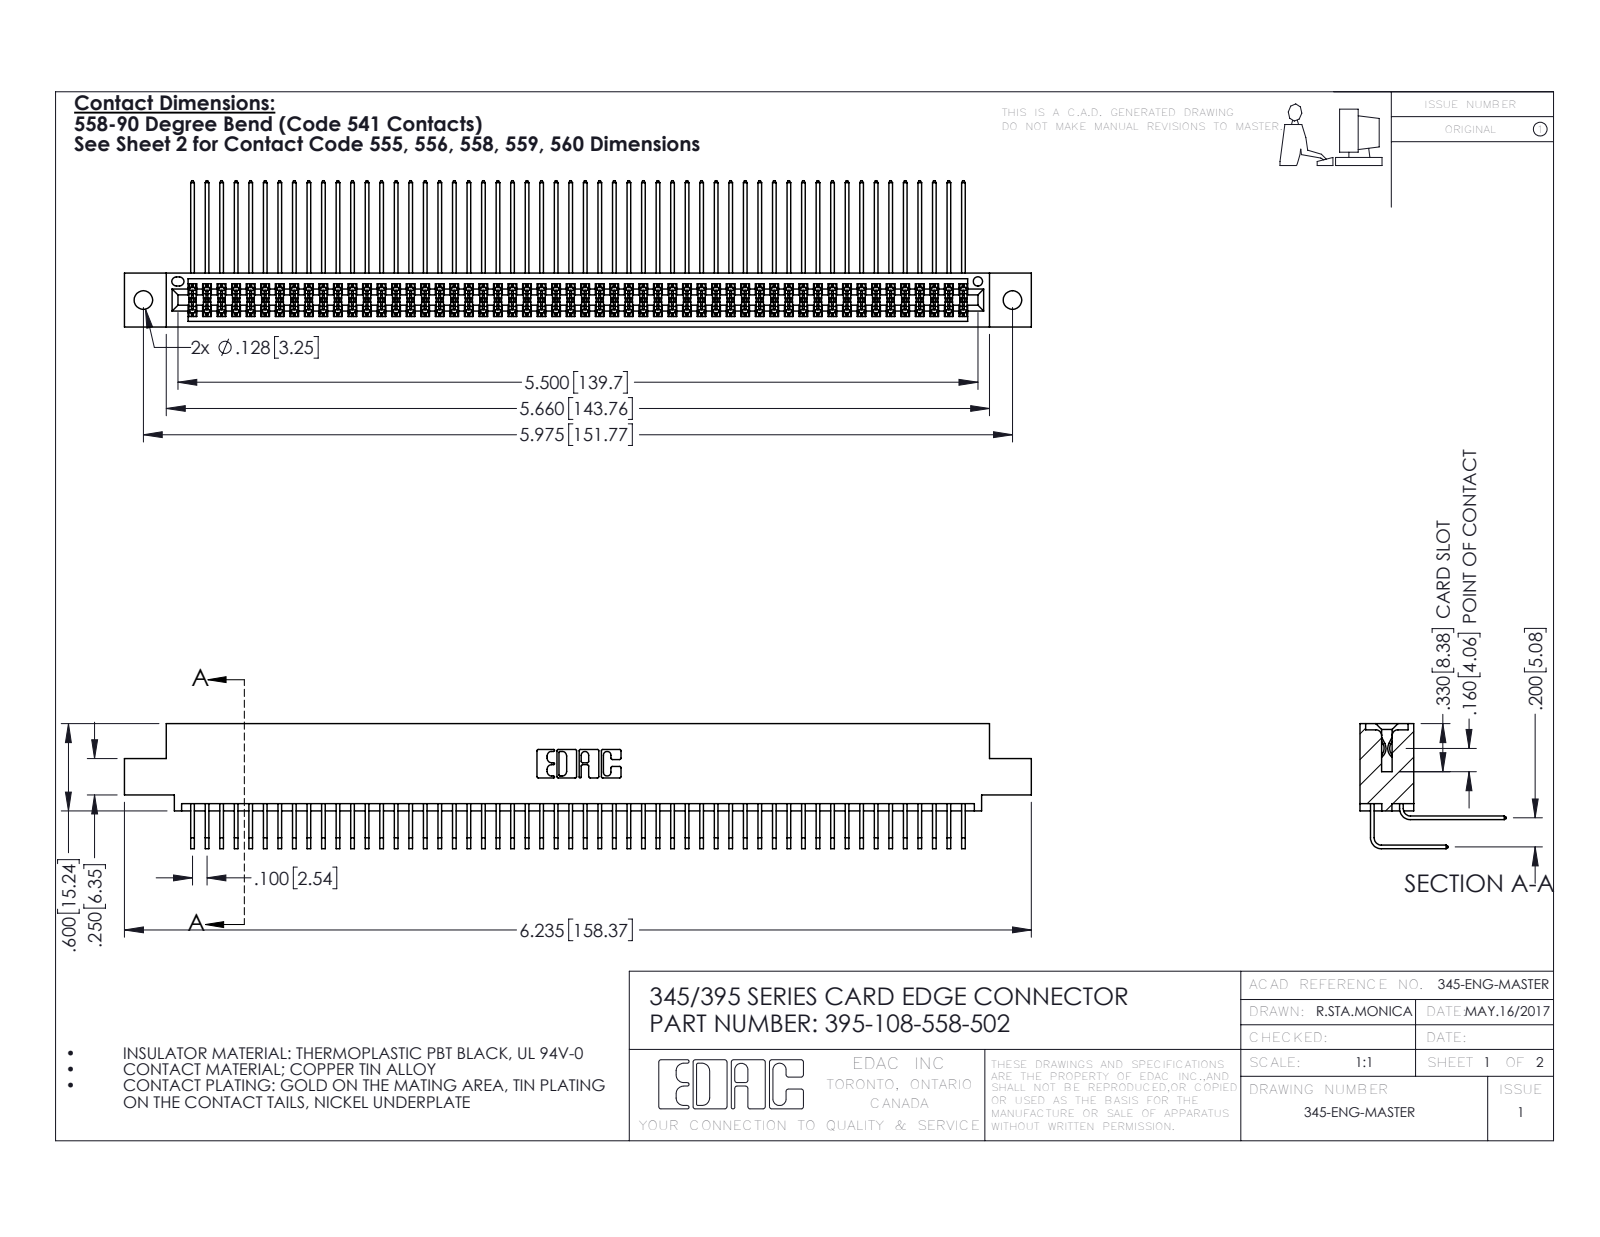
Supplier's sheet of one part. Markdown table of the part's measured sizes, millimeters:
| quantity | value |
| --- | --- |
| part name | 345-292-001_558 559 Tail - 1; 345 Part_0.110 Offset - 0.128 Dia; 345-292-001_558 Tail - 2; 395-108-558-502 |
| STEP written by | SolidWorks 2016 (CONFIG_CONTROL_DESIGN) |
| units | millimeters |
| bodies | 109 solids, 5746 faces (3864 planar, 1882 cylindrical, 0 other) |
| overall size | 158.4 × 25.5 × 21.8 |
| volume | 16 000 mm³ |
| surface area | 26 650 mm² |
| round holes (diameter × count) | 3.3 × 2, 1.6 × 1 |
| partial cylindrical surfaces (radius × count) | 0.2 × 162, 0.3 × 22, 0.2 × 6, 0.8 × 6, 0.7 × 3, 0.4 × 2, 0.5 × 2, 0.6 × 2 |
| main face-to-face distances | 1.8, 7.6, 5.1, 9.4, 2.5, 6.9, 0.6, 5.7, 0.6, 4.4 |
| hole center spacings | 6.9, 145.8, 151.8 |
